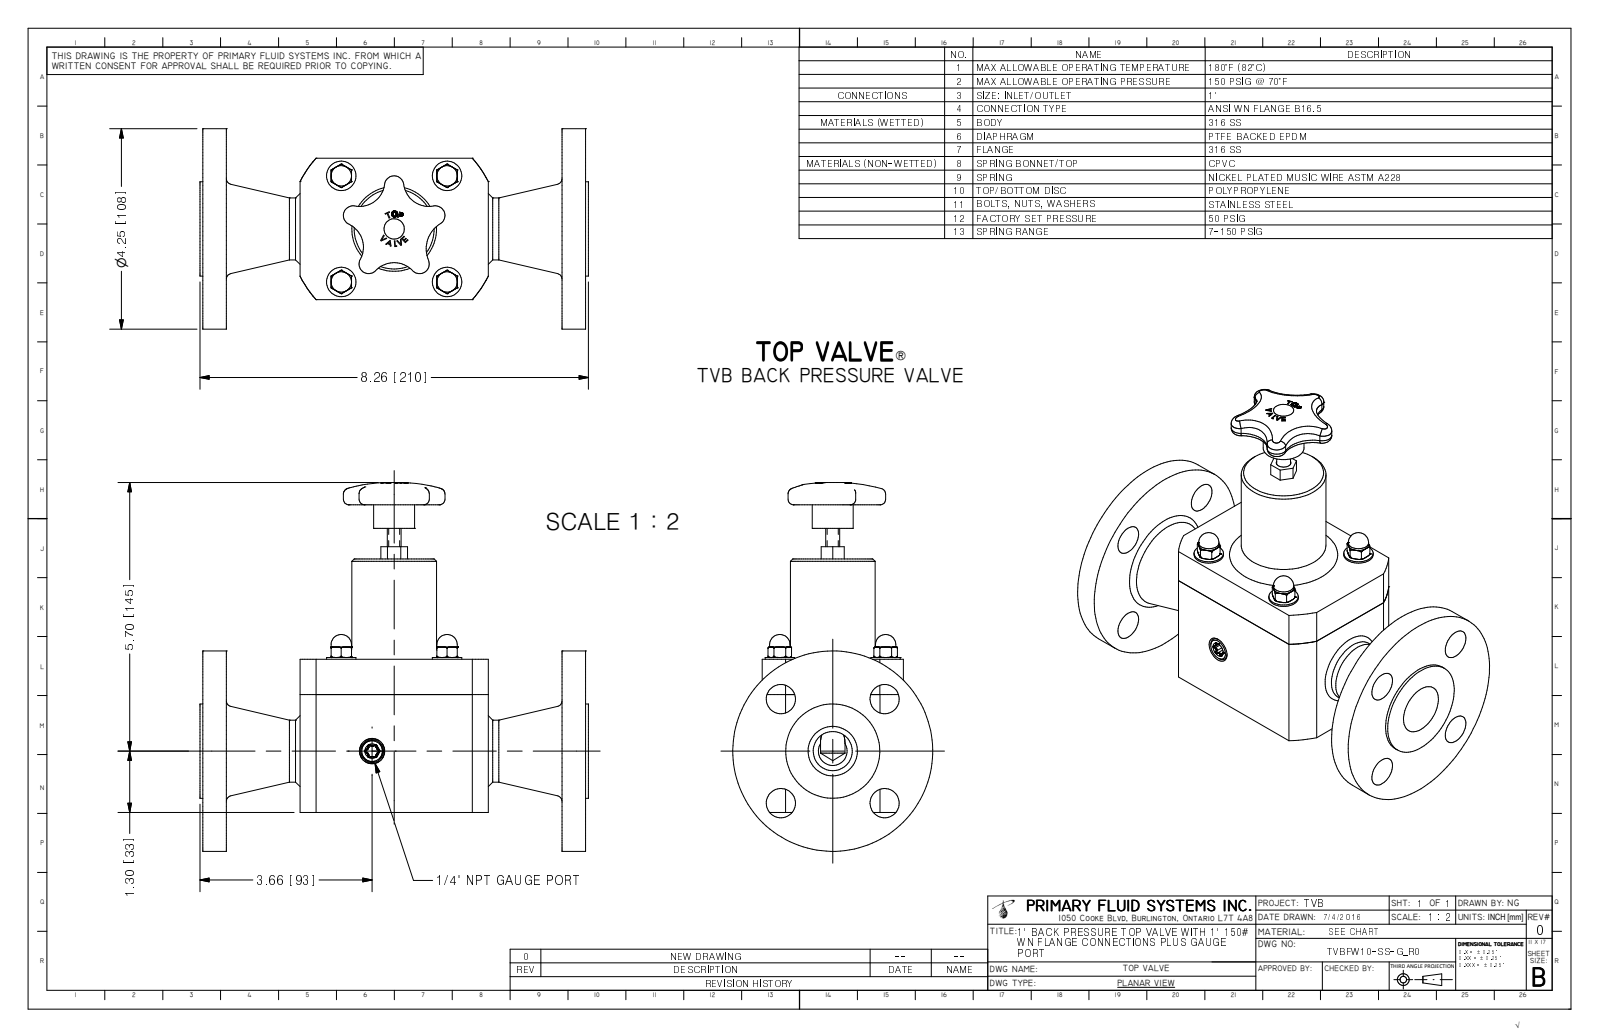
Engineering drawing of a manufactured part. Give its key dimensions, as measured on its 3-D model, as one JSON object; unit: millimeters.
{"part_name": "TVBFW10-SS-G-R0", "step_written_by": "Autodesk Inventor 2009 (AUTOMOTIVE_DESIGN)", "units": "millimeters", "bodies": {"solids": 1, "faces": 391, "planar": 162, "cylindrical": 69, "other": 160}, "overall_size": [209.8, 198.7, 108], "volume_mm3": 997300, "surface_area_mm2": 121500, "round_holes": [[4.4, 4], [15.7, 4], [26.6, 1]], "round_bosses_or_shafts": [[15.9, 4], [11, 4], [9.5, 4], [108, 1], [50.8, 1], [45.7, 1], [33.4, 1], [22.1, 1]], "partial_cylinders_radius": [[0.7, 6], [2.2, 5], [5.2, 5], [13.6, 4], [16.7, 4], [15.9, 1], [18.9, 1], [56.8, 1]], "face_to_face_distances": [12.7, 193.9, 76.2, 206.6, 52.5, 154.1, 39.8, 141.4, 181.2, 82.6], "hole_center_spacings": [39.6, 56, 57.2, 79.2, 80.8]}
